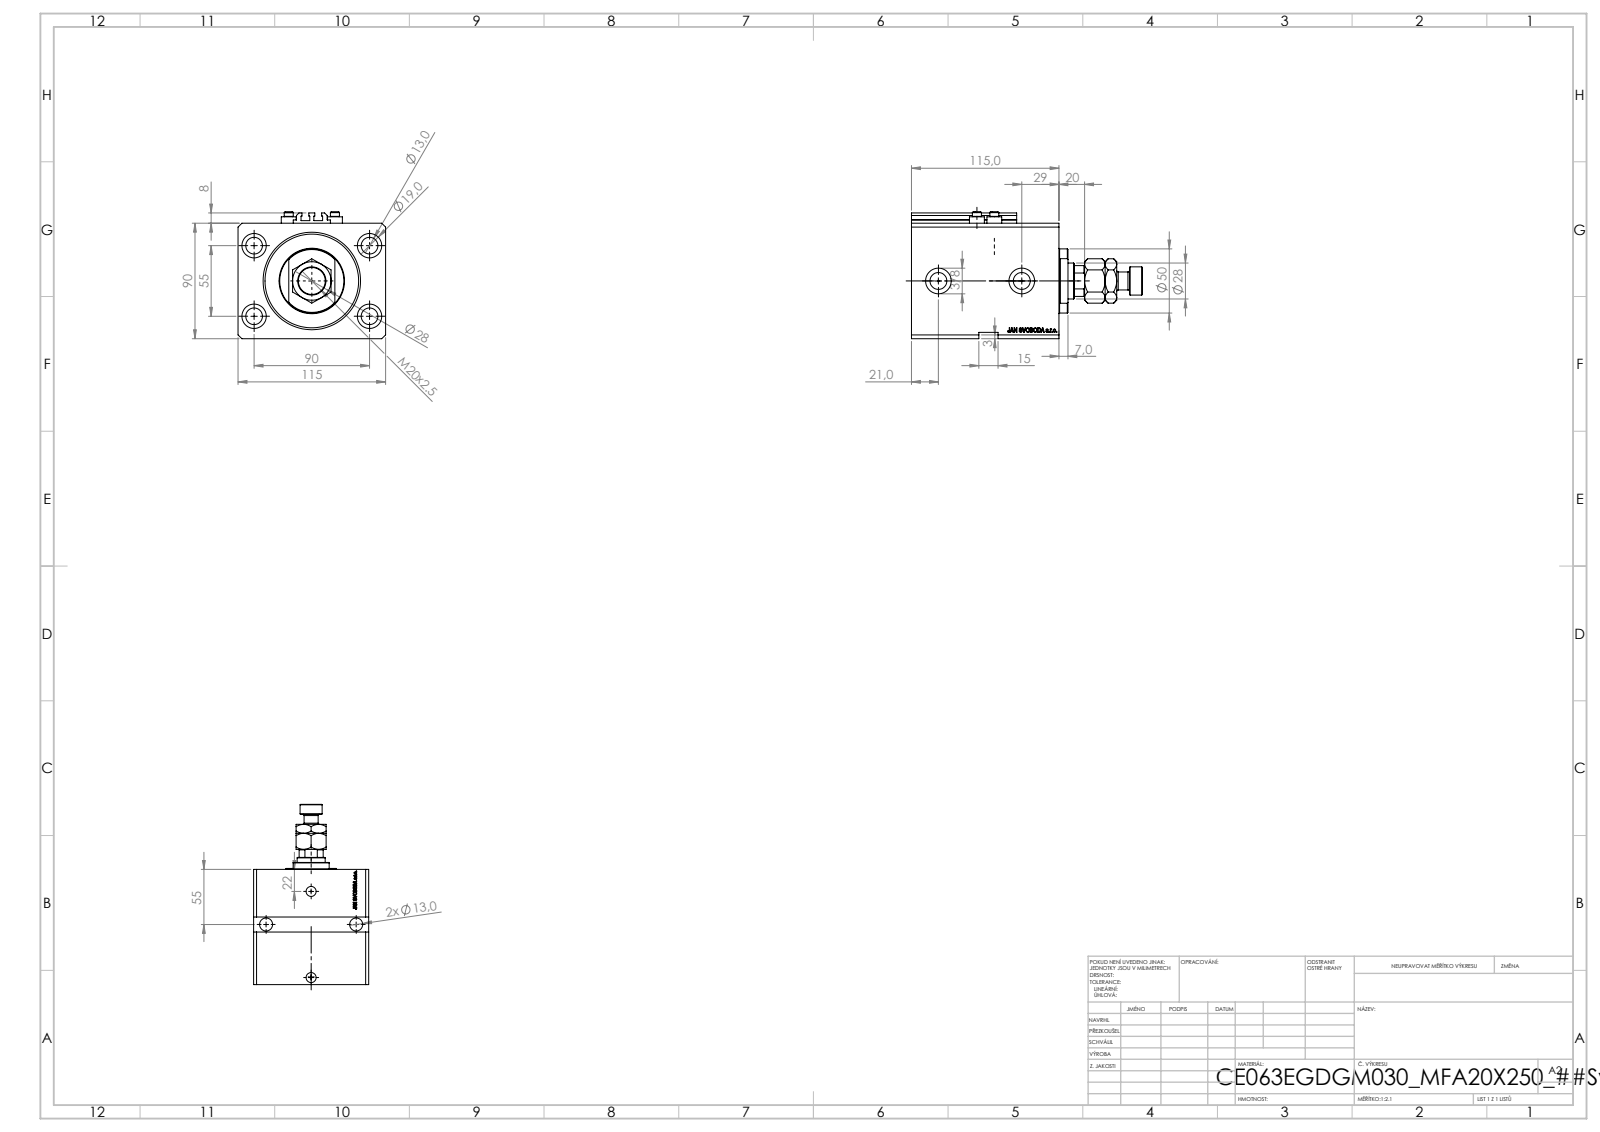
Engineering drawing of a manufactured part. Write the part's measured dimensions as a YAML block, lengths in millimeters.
part_name: "V250CE_E_Body; MFA; ALLEN BOLT V250CE; V250CE_C_VCP (+1 more)"
step_written_by: "SolidWorks 2019 (CONFIG_CONTROL_DESIGN)"
units: millimeters
bodies: {solids: 9, faces: 1175, planar: 563, cylindrical: 142, other: 470}
overall_size: [180, 115, 99]
volume: 1050000
surface_area: 170253
round_holes:
  - {diameter: 13, count: 6}
  - {diameter: 1.25, count: 4}
  - {diameter: 4, count: 4}
  - {diameter: 19, count: 4}
  - {diameter: 10, count: 2}
  - {diameter: 13.16, count: 2}
  - {diameter: 20, count: 2}
  - {diameter: 18.5, count: 1}
  - {diameter: 28, count: 1}
  - {diameter: 63, count: 1}
  - {diameter: 76, count: 1}
round_bosses_or_shafts:
  - {diameter: 11.6, count: 4}
  - {diameter: 7, count: 4}
  - {diameter: 50, count: 1}
  - {diameter: 22, count: 1}
  - {diameter: 14, count: 1}
partial_cylinders:
  - {radius: 0.2, count: 10}
  - {radius: 13.5, count: 1}
face_to_face_distances: [115, 90, 20, 97.1, 95, 17.9, 77.1, 30, 65, 13]
hole_center_spacings: [52.74, 90, 13.6, 27.39, 28.46, 33.62, 36, 38.48]
